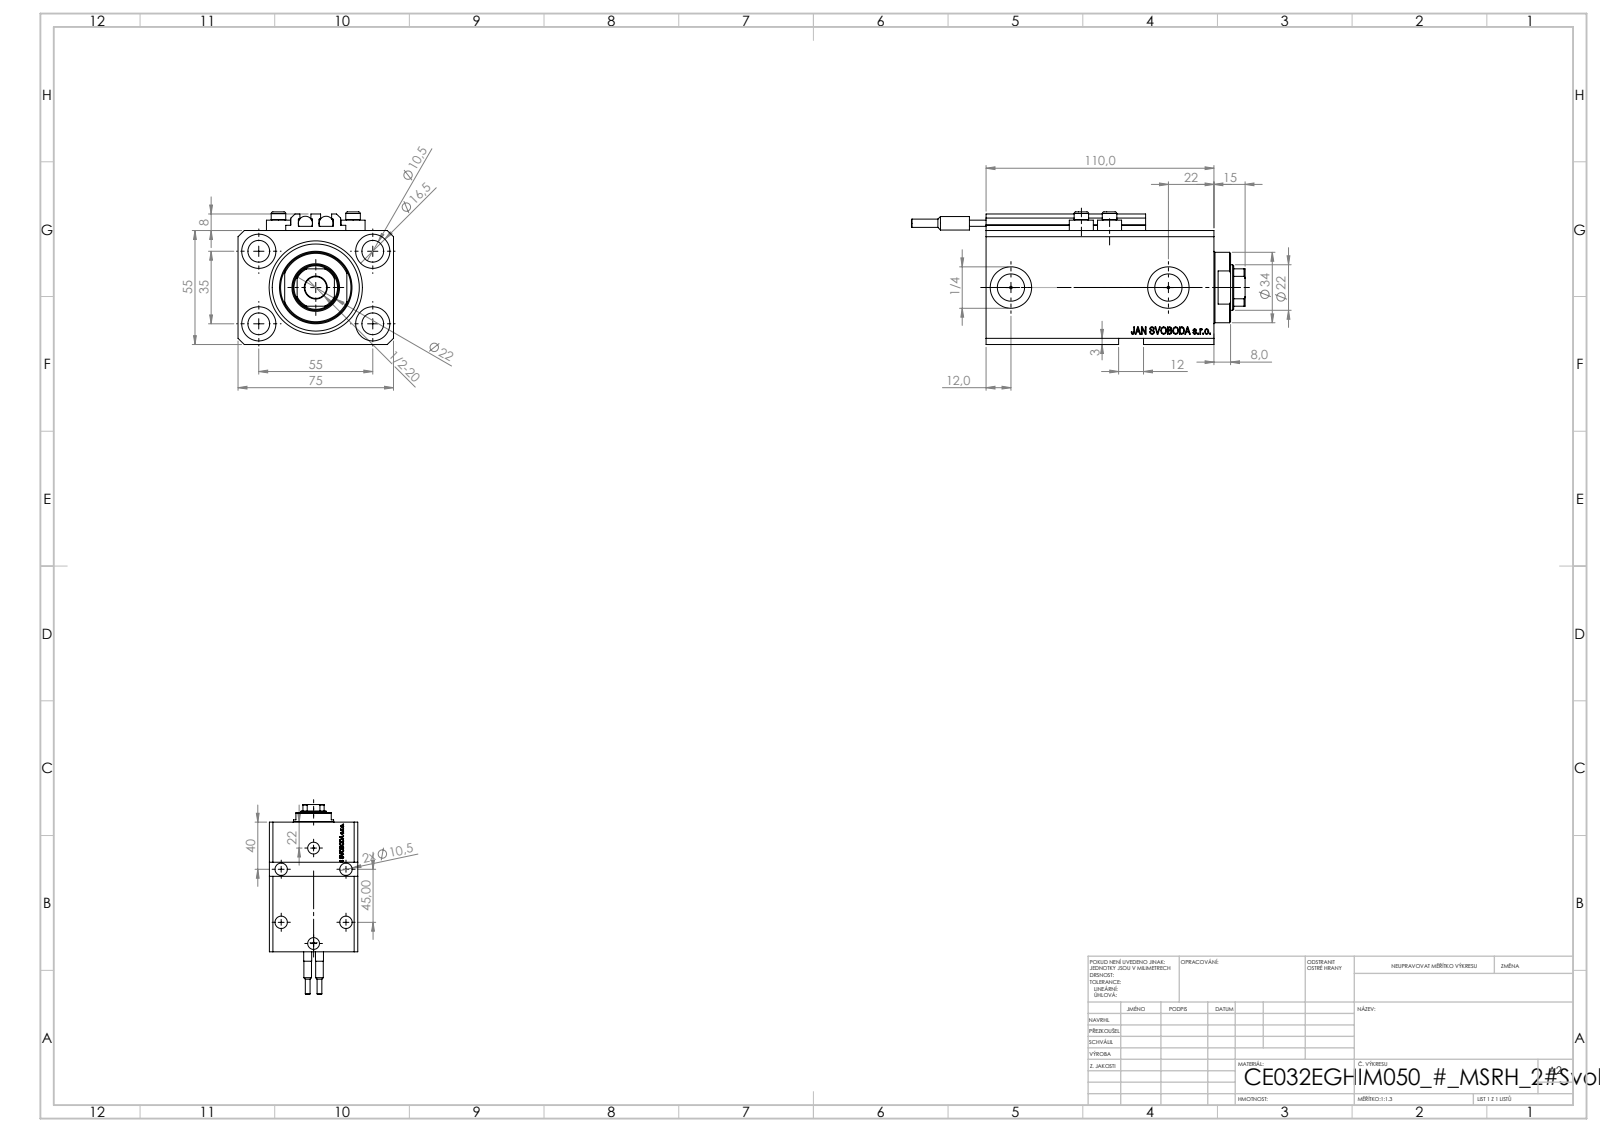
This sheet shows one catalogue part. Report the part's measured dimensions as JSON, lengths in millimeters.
{"part_name": "ALLEN BOLT V250CE; V250CE_VC_E; SWITCH_V250CE; V250CE_E_Body (+1 more)", "step_written_by": "SolidWorks 2019 (CONFIG_CONTROL_DESIGN)", "units": "millimeters", "bodies": {"solids": 10, "faces": 1136, "planar": 546, "cylindrical": 158, "other": 432}, "overall_size": [161, 75, 64], "volume_mm3": 384911, "surface_area_mm2": 98392, "round_holes": [[10.5, 9], [1.25, 4], [4, 4], [16.5, 4], [10, 2], [13.16, 2], [20, 2], [22, 1], [32, 1], [45, 1]], "round_bosses_or_shafts": [[11.6, 4], [7, 4], [6.8, 2], [6.5, 2], [4, 2], [34, 1]], "partial_cylinders_radius": [[0.2, 10], [10.5, 1]], "face_to_face_distances": [55, 75, 3, 15, 110, 57, 95, 9.9, 85.1, 100.1], "hole_center_spacings": [32.6, 32.87, 55, 68.74, 13.6, 14.09, 23.05, 25.81]}
